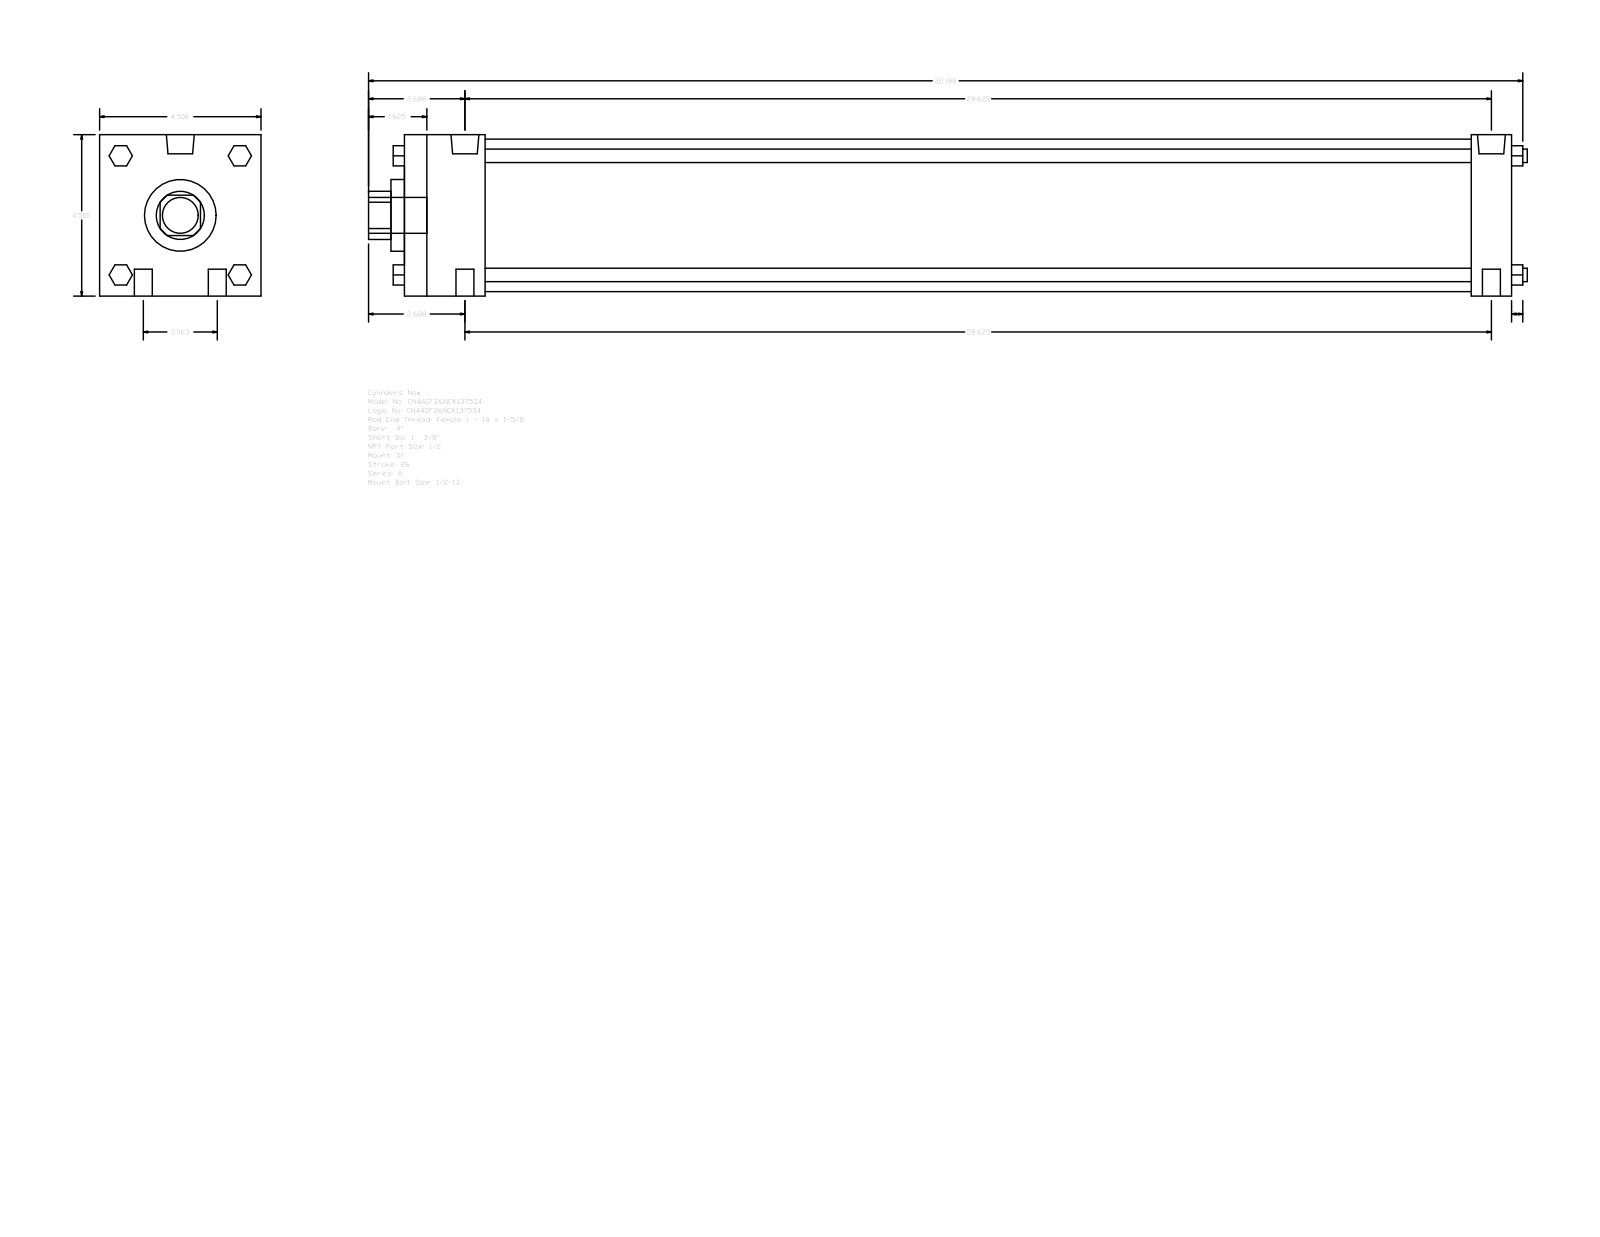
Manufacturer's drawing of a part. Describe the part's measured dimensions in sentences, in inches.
The part is named "A_SF__0400_1.375". Its 3-D file was written by "GSSL Pune (CONFIG_CONTROL_DESIGN)". It is 0 solids with 124 faces: 94 planar, 30 cylindrical and 0 other. Overall it measures 32.313 by 4.5 by 4.5 inches. Round holes: 1 of diameter 1.375, 1 of diameter 2, 1 of diameter 4.25. Round bosses or shafts: 4 of diameter 0.5, 4 of diameter 0.375, 2 of diameter 0.778, 2 of diameter 0.344, 1 of diameter 1. Partial cylindrical surfaces (rounded edges, fillets, slot ends): 1 of radius 0.672. The main face-to-face distances are 4.5, 30.875, 1.125, 29.75, 2.25, 27.5, 28.625, 0.563, 0.375, 2.625.
